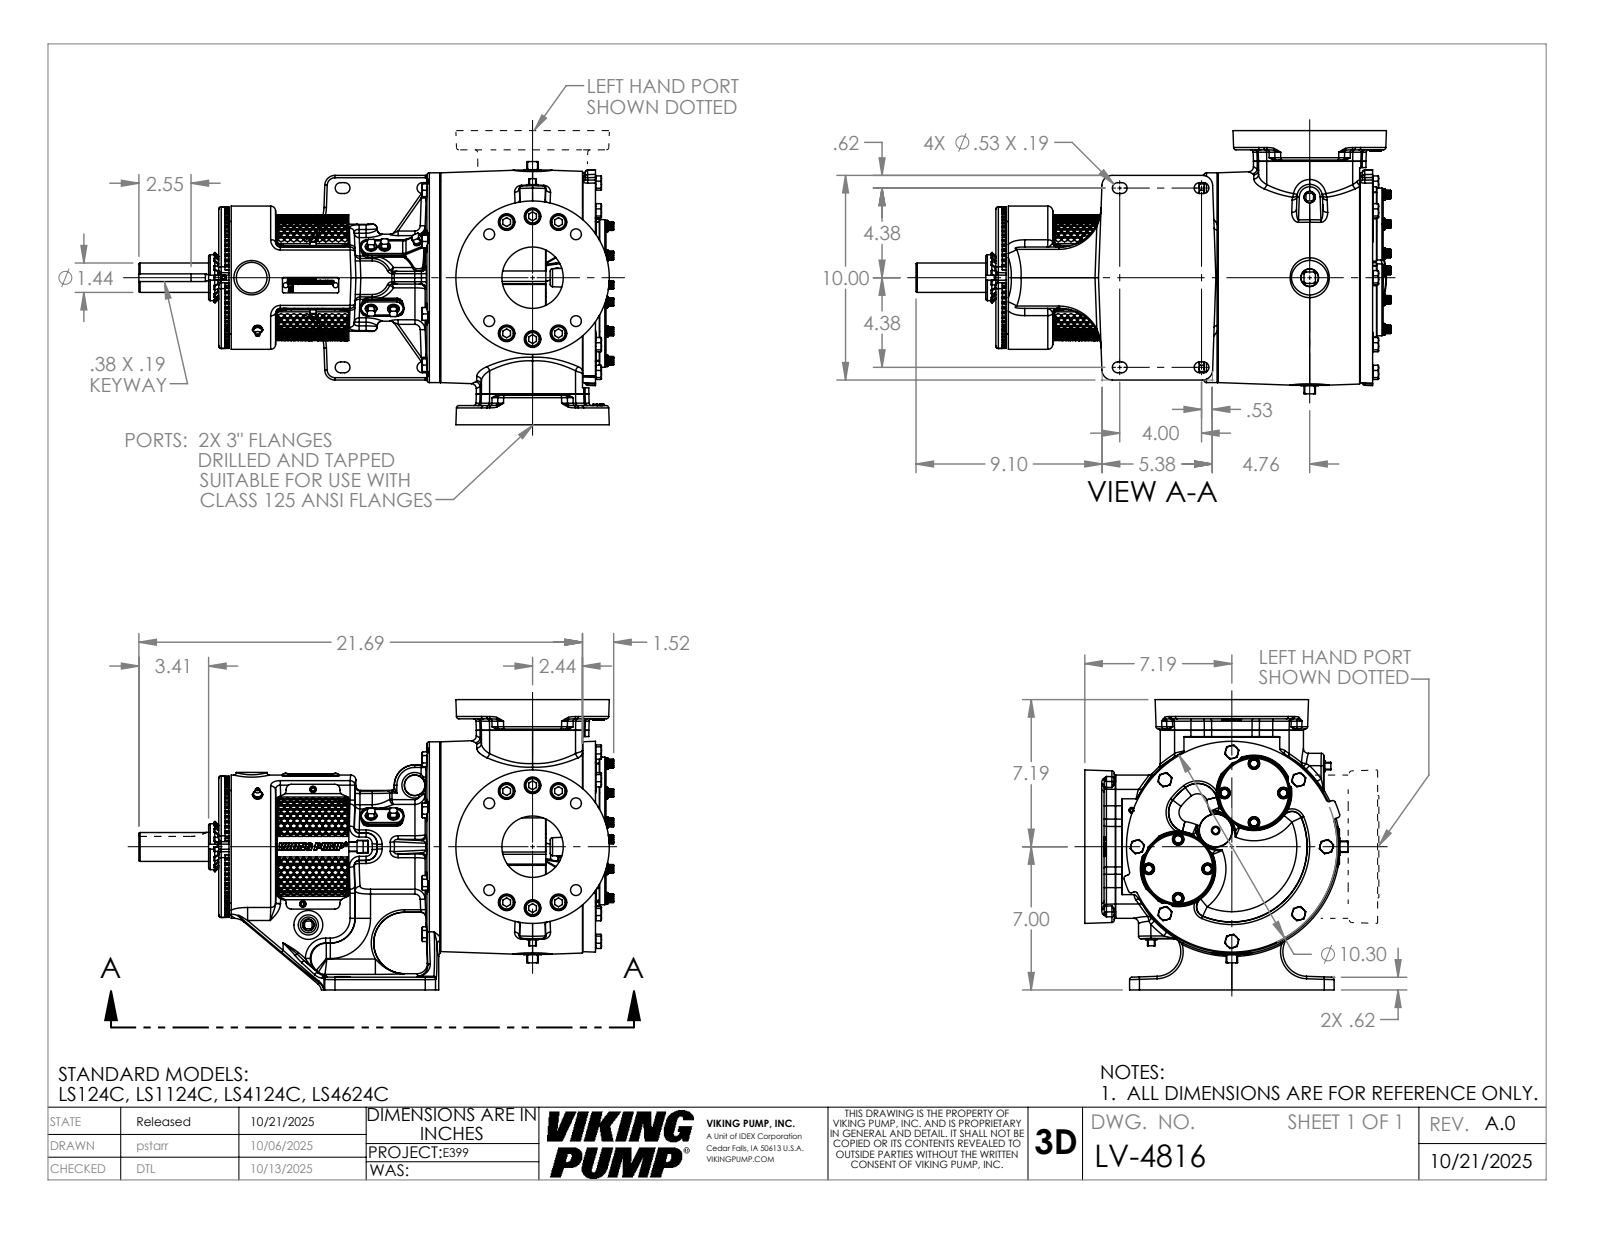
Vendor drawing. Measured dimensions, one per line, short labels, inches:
name: LV-4816
written by: SolidWorks 2024 (AUTOMOTIVE_DESIGN)
unit: in
bodies: 1 solid, 5555 faces (1731 planar, 1098 cylindrical, 2726 other)
size: 23.211 × 14.187 × 12.863
volume: 1 105 in³; area: 1 420 in²
holes: 12× ⌀0.812, 9× ⌀0.25, 8× ⌀0.531, 8× ⌀1.094, 6× ⌀0.199, 3× ⌀0.159, 2× ⌀0.266, 2× ⌀0.313, 2× ⌀3, 1× ⌀0.453, 1× ⌀1.506, 1× ⌀1.578
bosses: 12× ⌀0.75, 10× ⌀0.625, 8× ⌀0.563, 6× ⌀0.625, 3× ⌀0.312, 3× ⌀0.19, 2× ⌀3.5, 1× ⌀10.25
rounds: 109× R0.063, 82× R0.12, 74× R0.069, 56× R0.01, 48× R0.24, 20× R0.03, 16× R1, 14× R0.5
face distances: 14.187, 0.5, 12.128, 3.541, 15.669, 16.184, 12.643, 0.515, 2.25, 1.382
hole spacings: 3, 4.243, 6, 1.375, 1.042, 1.298, 2.18, 2.296
